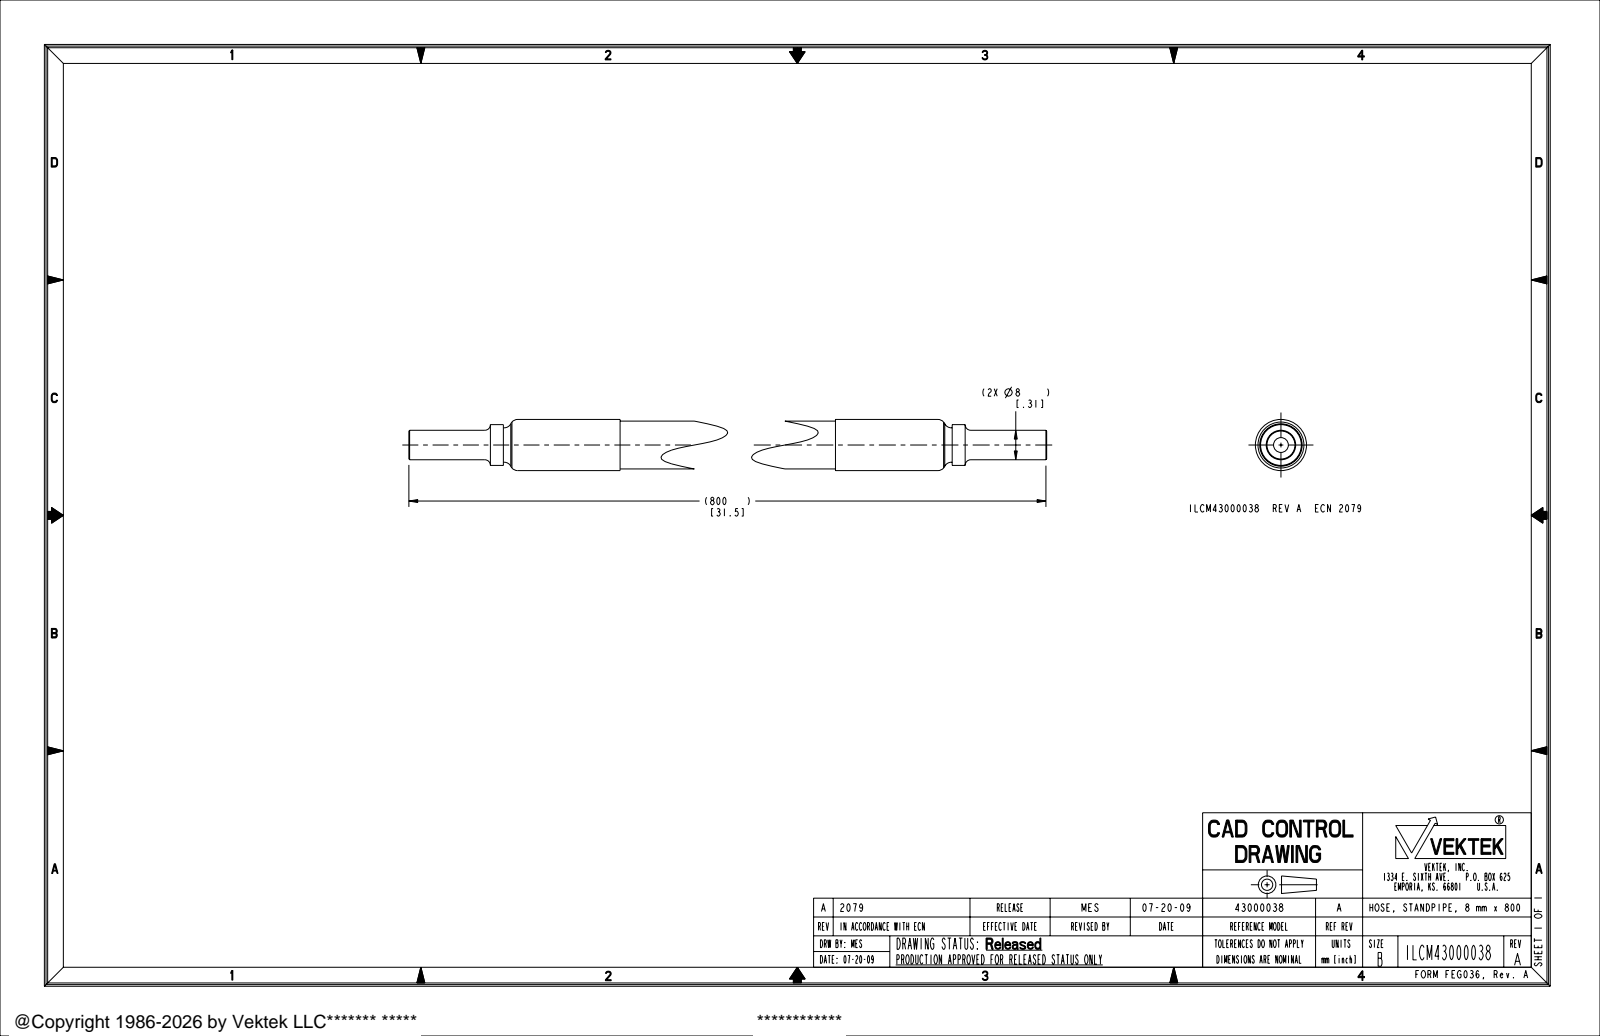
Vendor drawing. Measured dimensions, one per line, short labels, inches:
name: ILCM43000038
written by: PRO/ENGINEER BY PARAMETRIC TECHNOLOGY CORPORATION, 2007460 (AUTOMOTIVE_DESIGN_CC2)
unit: in
bodies: 1 solid, 74 faces (14 planar, 28 cylindrical, 32 other)
size: 31.496 × 0.543 × 0.543
volume: 4.91 in³; area: 79.49 in²
holes: 1× ⌀0.157, 1× ⌀0.236, 1× ⌀0.512
bosses: 1× ⌀0.543, 1× ⌀0.508, 1× ⌀0.433, 1× ⌀0.354, 1× ⌀0.313
face distances: 0.073, 29.156, 29.228, 29.083, 1.134, 1.207, 30.289, 30.362, 1.004, 30.492
